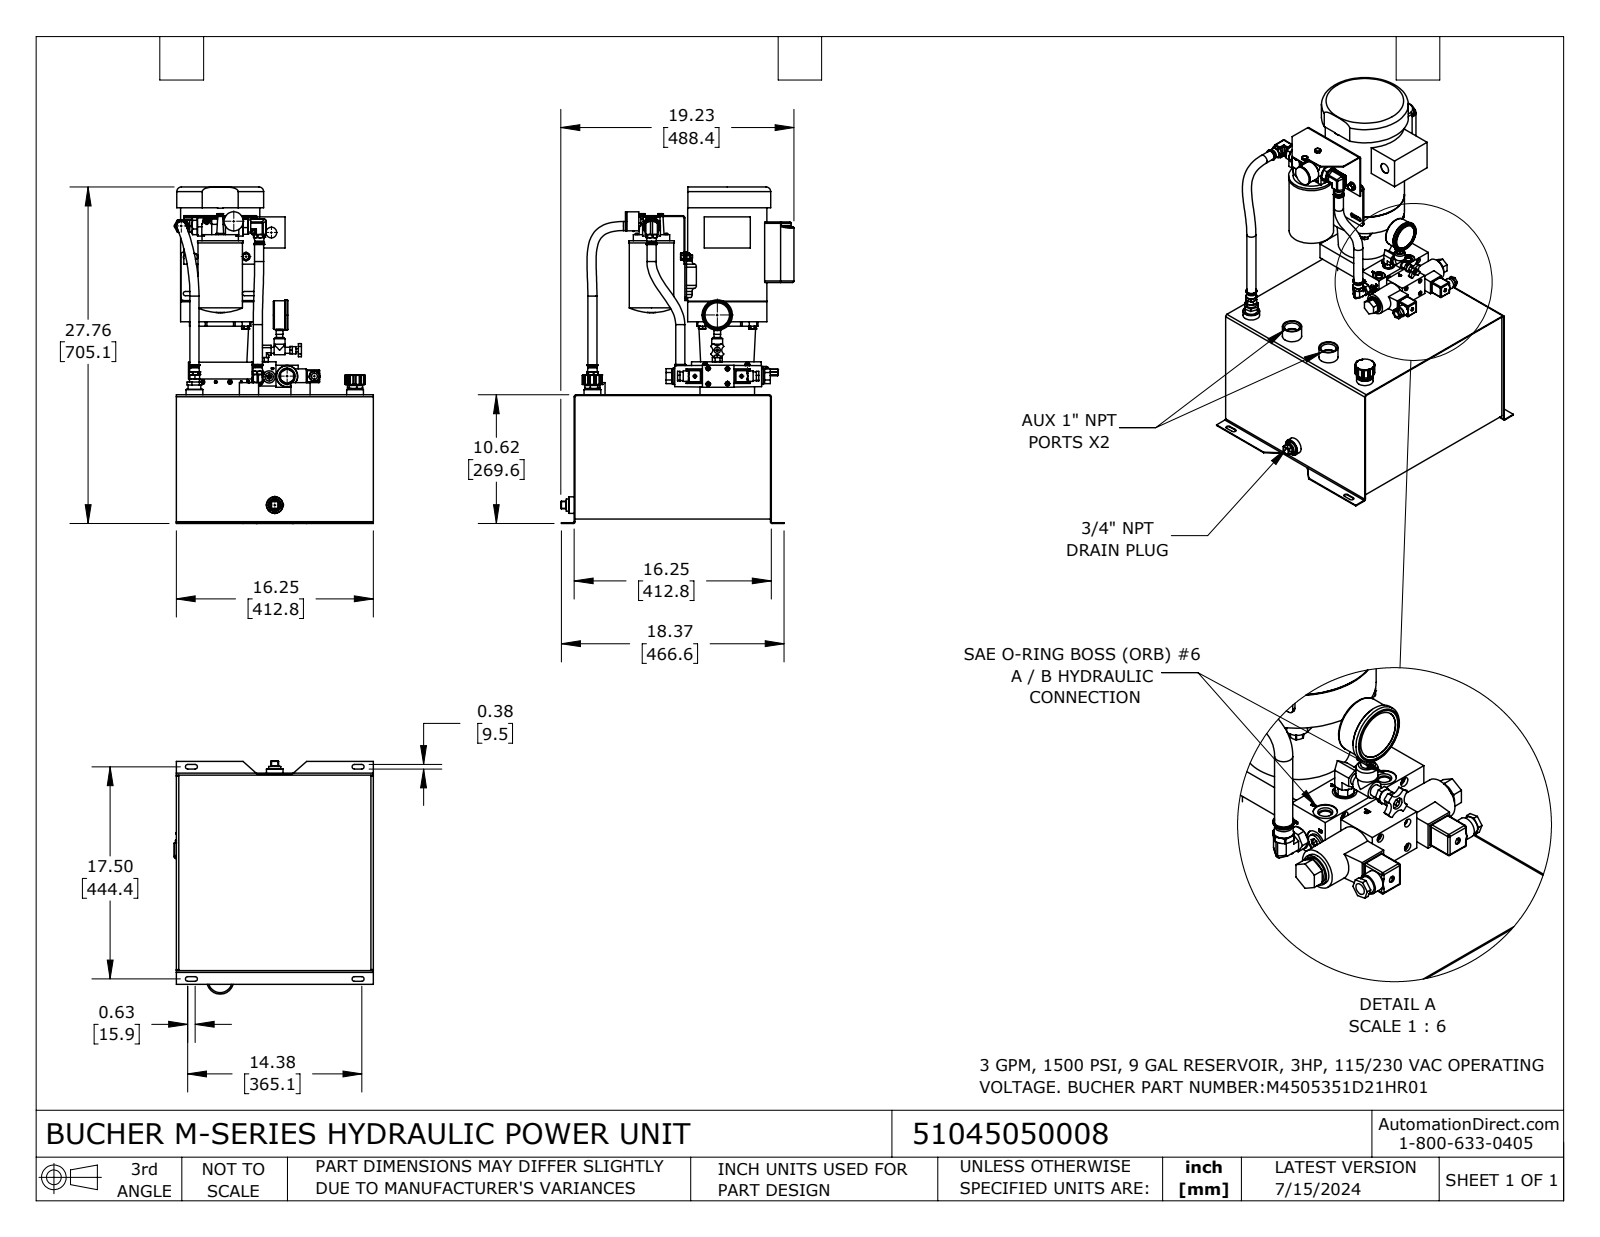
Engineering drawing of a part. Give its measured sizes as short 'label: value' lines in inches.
name: 51045050008
written by: SolidWorks 2023 (CONFIG_CONTROL_DESIGN)
unit: in
bodies: 57 solids, 3855 faces (1675 planar, 1085 cylindrical, 1095 other)
size: 27.758 × 19.227 × 16.421
volume: 786.7 in³; area: 3 825 in²
holes: 9× ⌀0.25, 9× ⌀1, 8× ⌀0.313, 8× ⌀0.469, 8× ⌀0.511, 6× ⌀0.225, 6× ⌀0.5, 5× ⌀0.281, 4× ⌀0.17, 4× ⌀0.203, 4× ⌀0.228, 4× ⌀0.266
bosses: 7× ⌀0.37, 7× ⌀0.246, 5× ⌀0.367, 5× ⌀0.187, 4× ⌀0.9, 4× ⌀0.75, 4× ⌀0.738, 4× ⌀0.68
rounds: 24× R0.039, 24× R0.05, 23× R0.105, 20× R0.02, 20× R0.025, 16× R0.12, 16× R0.25, 14× R0.07
face distances: 0.066, 16.186, 0.125, 15.725, 0.125, 10.25, 10.125, 10.184, 10.059, 16.252
hole spacings: 4.381, 2.937, 1.575, 1.781, 1.781, 2.098, 2.098, 4.154
